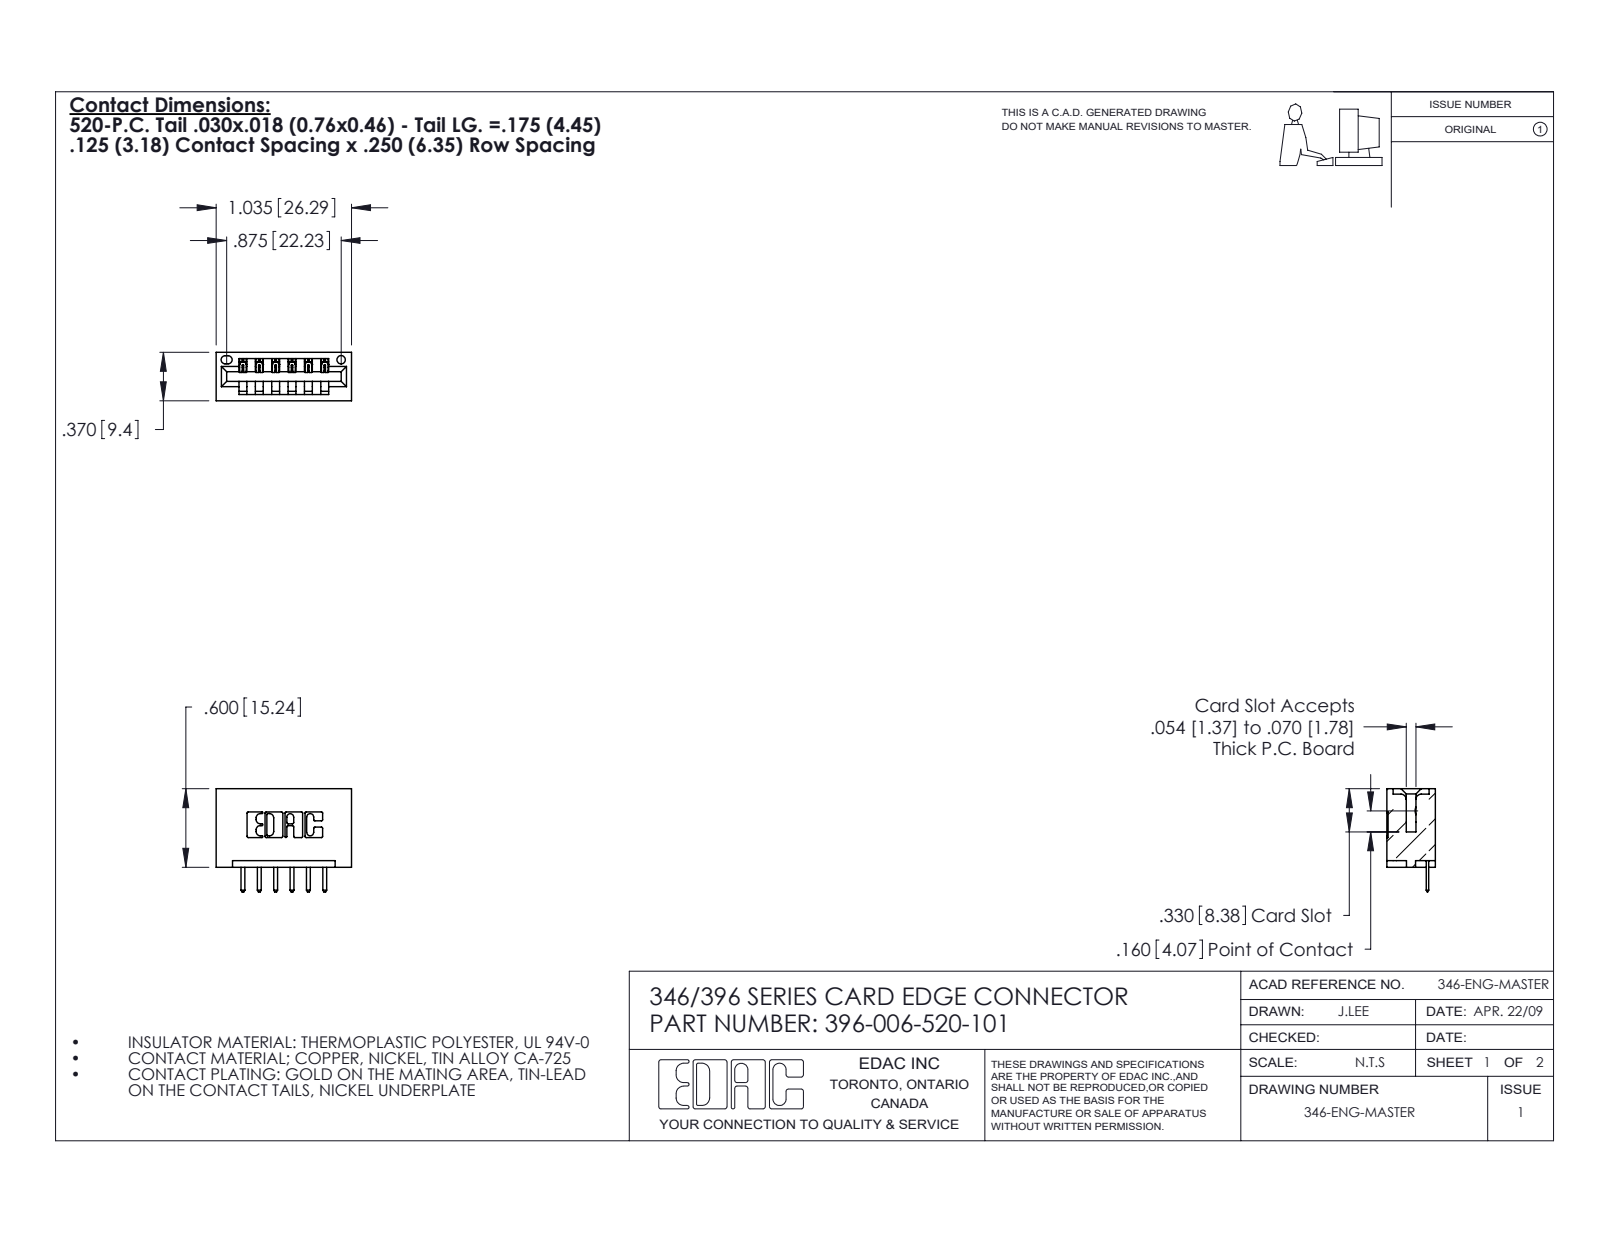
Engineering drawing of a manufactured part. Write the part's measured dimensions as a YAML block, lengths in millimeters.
part_name: "396-006-520-101; 345-292-001_345-293-120; 346 Part_No Mounting Lugs"
step_written_by: "SolidWorks 2020 (CONFIG_CONTROL_DESIGN)"
units: millimeters
bodies: {solids: 7, faces: 486, planar: 324, cylindrical: 162, other: 0}
overall_size: [26.3, 20, 9.4]
volume: 2800
surface_area: 3130
round_holes:
  - {diameter: 1.6, count: 1}
partial_cylinders:
  - {radius: 0.3, count: 22}
  - {radius: 0.3, count: 14}
  - {radius: 0.2, count: 12}
  - {radius: 0.2, count: 6}
  - {radius: 0.8, count: 6}
  - {radius: 0.7, count: 3}
  - {radius: 0.8, count: 2}
  - {radius: 1, count: 2}
face_to_face_distances: [6.4, 9.4, 1.2, 8.2, 3.8, 5.6, 2.5, 4.4, 3.2, 3.2]
